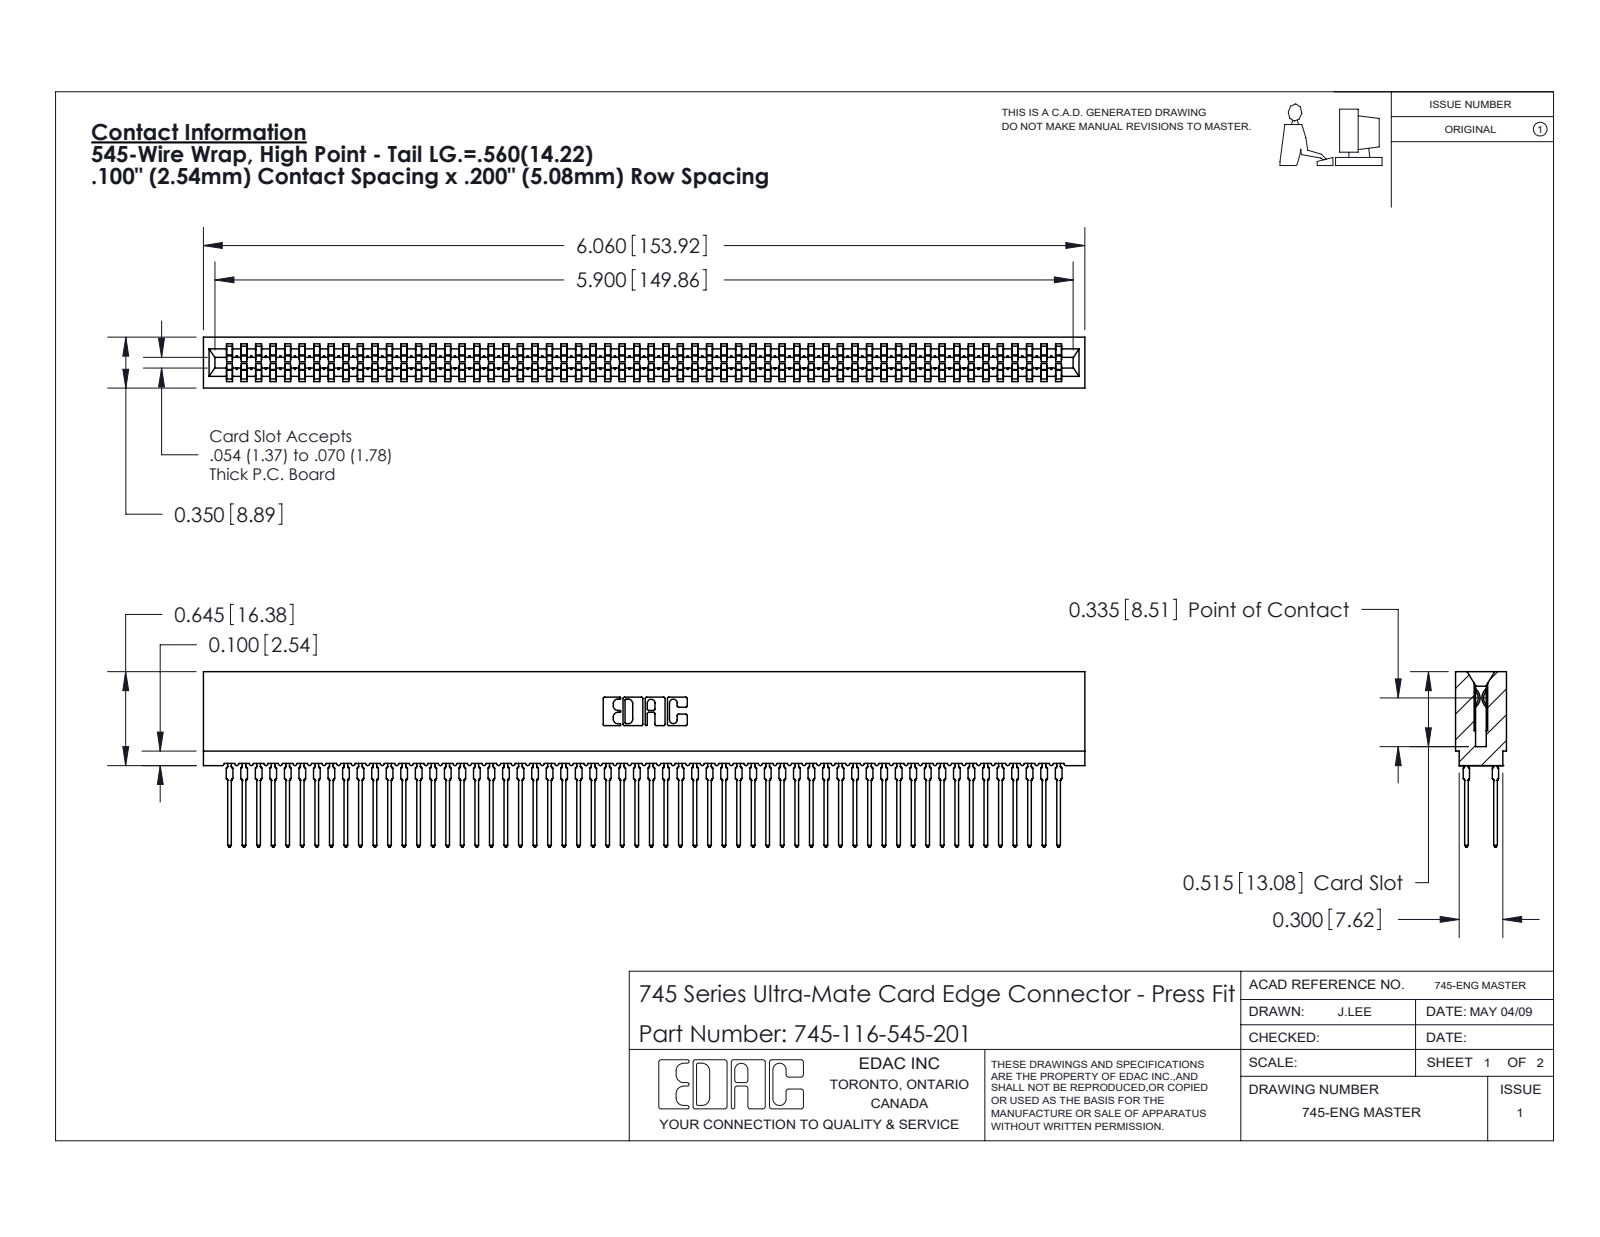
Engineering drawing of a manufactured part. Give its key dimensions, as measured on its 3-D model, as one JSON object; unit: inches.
{"part_name": "745-292-001_545; 745-116-545-201; 745 Part_Insulator Option - 01", "step_written_by": "SolidWorks 2020 (CONFIG_CONTROL_DESIGN)", "units": "inches", "bodies": {"solids": 117, "faces": 10477, "planar": 5391, "cylindrical": 2070, "other": 3016}, "overall_size": [6.06, 1.206, 0.35], "volume_in3": 0.865, "surface_area_in2": 47.98, "partial_cylinders_radius": [[0.021, 232], [0.015, 116], [0.01, 22], [0.005, 8], [0.011, 8], [0.007, 6], [0.031, 6], [0.026, 3]], "face_to_face_distances": [0.063, 0.287, 0.35, 0.2, 0.045, 0.305, 0.018, 0.243, 0.138, 0.212]}
